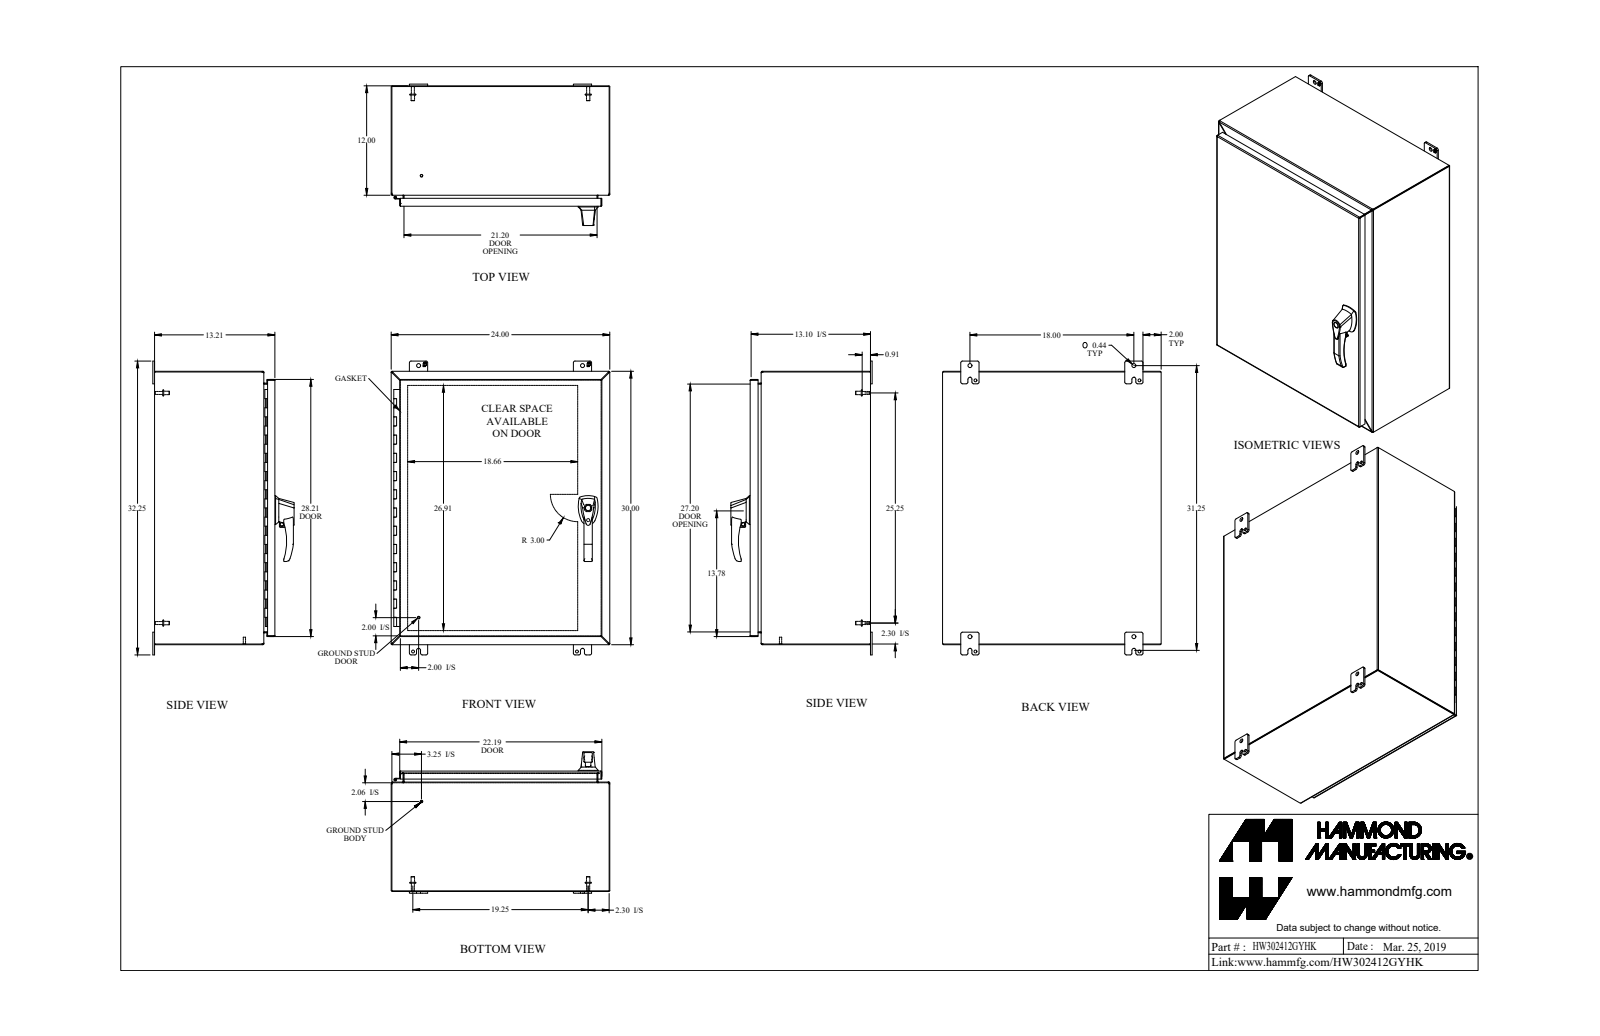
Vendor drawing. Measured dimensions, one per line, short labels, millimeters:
name: HW302412GYHK
written by: SolidWorks 2018 (AUTOMOTIVE_DESIGN)
unit: mm
bodies: 43 solids, 1453 faces (699 planar, 589 cylindrical, 165 other)
size: 819.2 × 609.6 × 394
volume: 4 134 000 mm³; area: 4 235 000 mm²
holes: 6× ⌀4.5, 4× ⌀6.4, 4× ⌀8, 3× ⌀5, 3× ⌀6.7, 3× ⌀10.5, 2× ⌀6.5, 2× ⌀10, 2× ⌀11.1, 1× ⌀4.7, 1× ⌀5.9, 1× ⌀8.5
bosses: 9× ⌀9.5, 6× ⌀6.4, 6× ⌀4, 4× ⌀16.5, 4× ⌀8.4, 3× ⌀25.4, 2× ⌀16, 2× ⌀13
rounds: 31× R6.4, 24× R4.8, 18× R0.9, 18× R2.7, 12× R1.5, 9× R3.2, 8× R1, 8× R5.5
face distances: 1.8, 607.8, 1.8, 333.7, 331.9, 335.5, 333.7, 760.2, 605.9, 609.6
hole spacings: 282.4, 282.4, 564.8, 28.2, 246.3, 282.4, 457.2, 797.1
